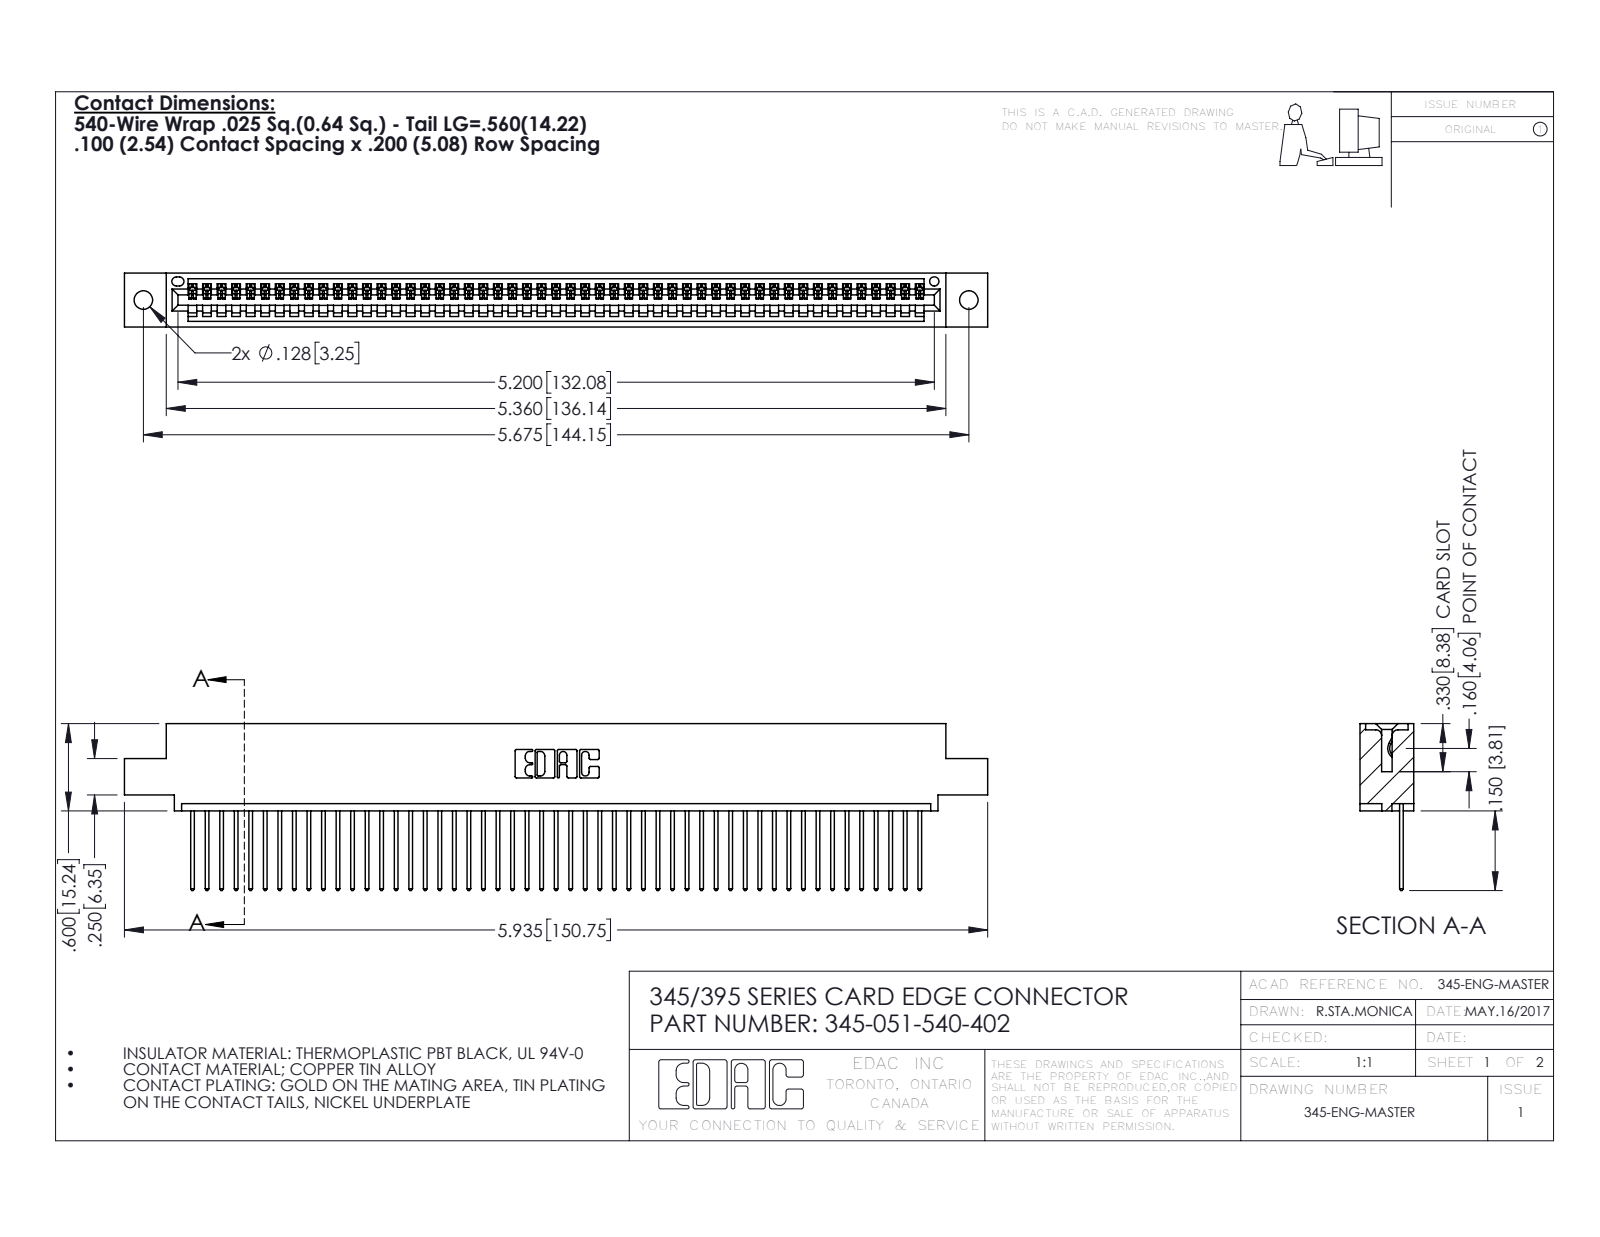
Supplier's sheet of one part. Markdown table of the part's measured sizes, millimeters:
| quantity | value |
| --- | --- |
| part name | 345-051-540-402; 345-292-001_345-293-140; 345 Part_0.110 Offset - 0.128 Dia |
| STEP written by | SolidWorks 2016 (CONFIG_CONTROL_DESIGN) |
| units | millimeters |
| bodies | 52 solids, 3088 faces (2124 planar, 964 cylindrical, 0 other) |
| overall size | 150.7 × 29.1 × 9.4 |
| volume | 14 400 mm³ |
| surface area | 19 500 mm² |
| round holes (diameter × count) | 3.3 × 2, 1.6 × 1 |
| partial cylindrical surfaces (radius × count) | 0.2 × 102, 0.3 × 102, 0.3 × 22, 0.2 × 6, 0.8 × 6, 0.7 × 3, 0.8 × 2, 1 × 2 |
| main face-to-face distances | 7.6, 1.8, 9.4, 2.5, 6.9, 0.6, 5.1, 5.7, 3.8, 1.8 |
| hole center spacings | 6.9, 138.2, 144.1 |
